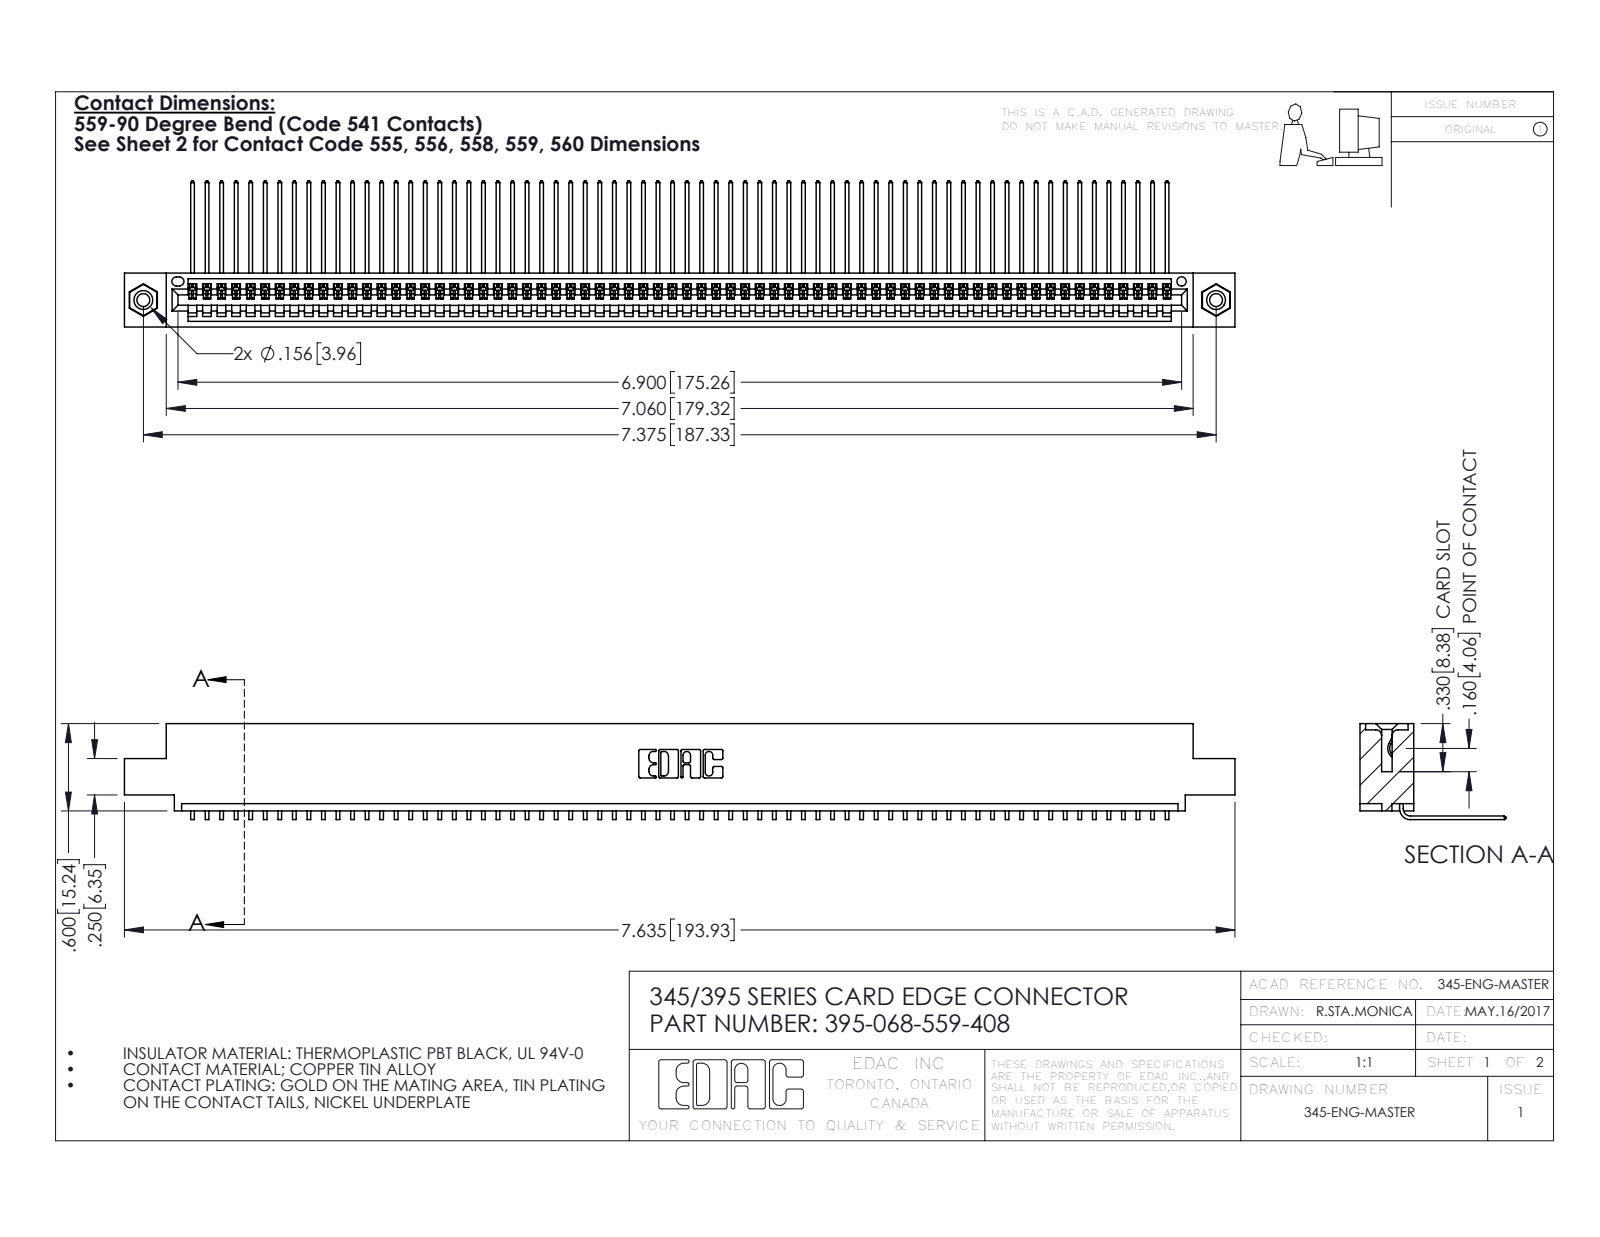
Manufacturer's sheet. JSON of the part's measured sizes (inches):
{"part_name": "345 Part_0.110 Offset - 0.156 Dia-TI; 395-068-559-408; 345-250-001_345-250-003-102; 345-292-001_558 559 Tail - 1", "step_written_by": "SolidWorks 2016 (CONFIG_CONTROL_DESIGN)", "units": "inches", "bodies": {"solids": 71, "faces": 4270, "planar": 2972, "cylindrical": 1282, "other": 16}, "overall_size": [7.635, 1.005, 0.659], "volume_in3": 1.146, "surface_area_in2": 41.45, "round_holes": [[0.089, 2], [0.125, 2], [0.156, 2], [0.064, 1]], "round_bosses_or_shafts": [[0.155, 2]], "partial_cylinders_radius": [[0.006, 136], [0.01, 22], [0.007, 6], [0.031, 6], [0.026, 3], [0.031, 2], [0.04, 2], [0.014, 1]], "face_to_face_distances": [0.072, 0.298, 0.37, 0.2, 0.098, 0.272, 0.025, 0.225, 0.149, 0.072], "hole_center_spacings": [0.27, 7.139, 7.375]}
